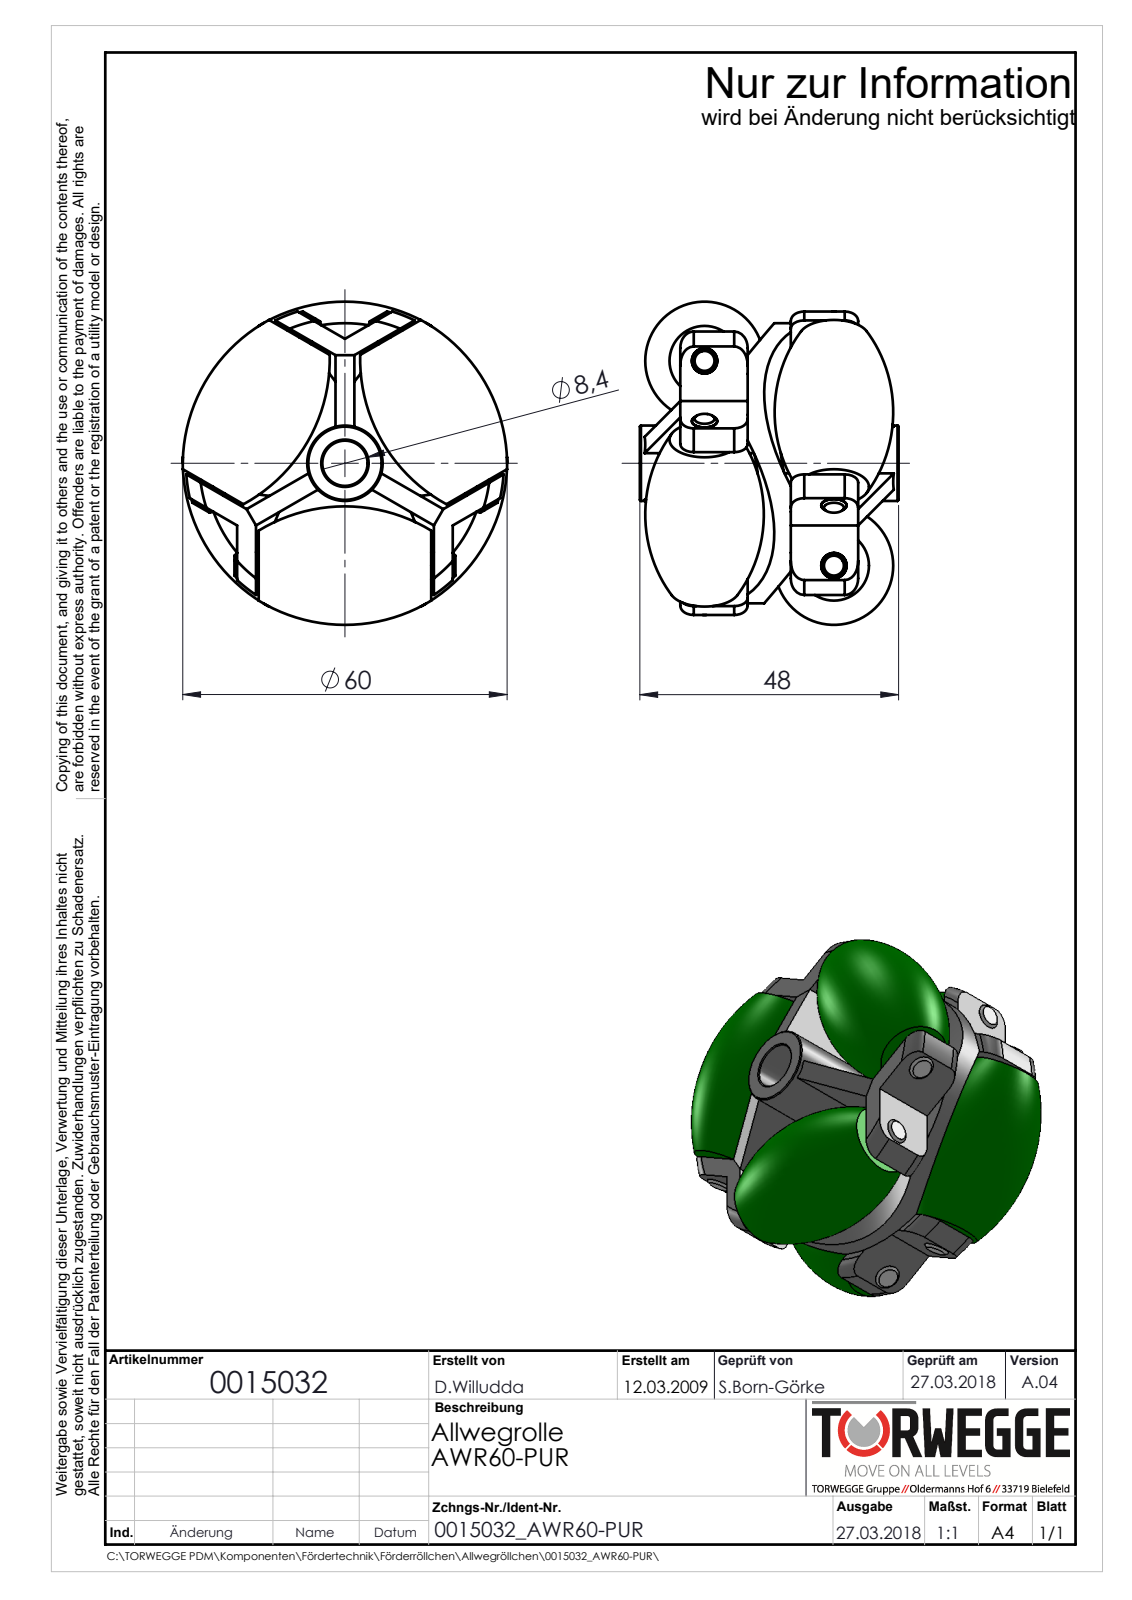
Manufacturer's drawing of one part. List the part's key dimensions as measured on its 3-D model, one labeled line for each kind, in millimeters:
Part name (STEP PRODUCT): AWR60_Röllchen-PUR; 0015032_AWR60-PUR; AWR60_Halter; AWR60_Stift
STEP written by: SolidWorks 2016 (AUTOMOTIVE_DESIGN)
Units: millimetres
Bodies: 13 solids, 282 faces (116 planar, 92 cylindrical, 74 other)
Overall size (bounding box): 60.19 × 60 × 48
Volume: 79 639 mm³ · Surface area: 35 250 mm²
Round holes (diameter × count): ⌀4.7 ×6, ⌀5.2 ×6, ⌀8.4 ×1
Round bosses / shafts (diameter × count): ⌀5 ×6, ⌀52 ×1, ⌀14 ×1
Partial cylindrical surfaces — rounded edges, fillets, slot ends (radius × count): R29.5 ×1
Main face-to-face distances: 18.25, 3.5, 14.75, 0.5, 4, 36.5, 32.5, 14.25, 17.75, 21.75
Hole centre spacings: 44.94
